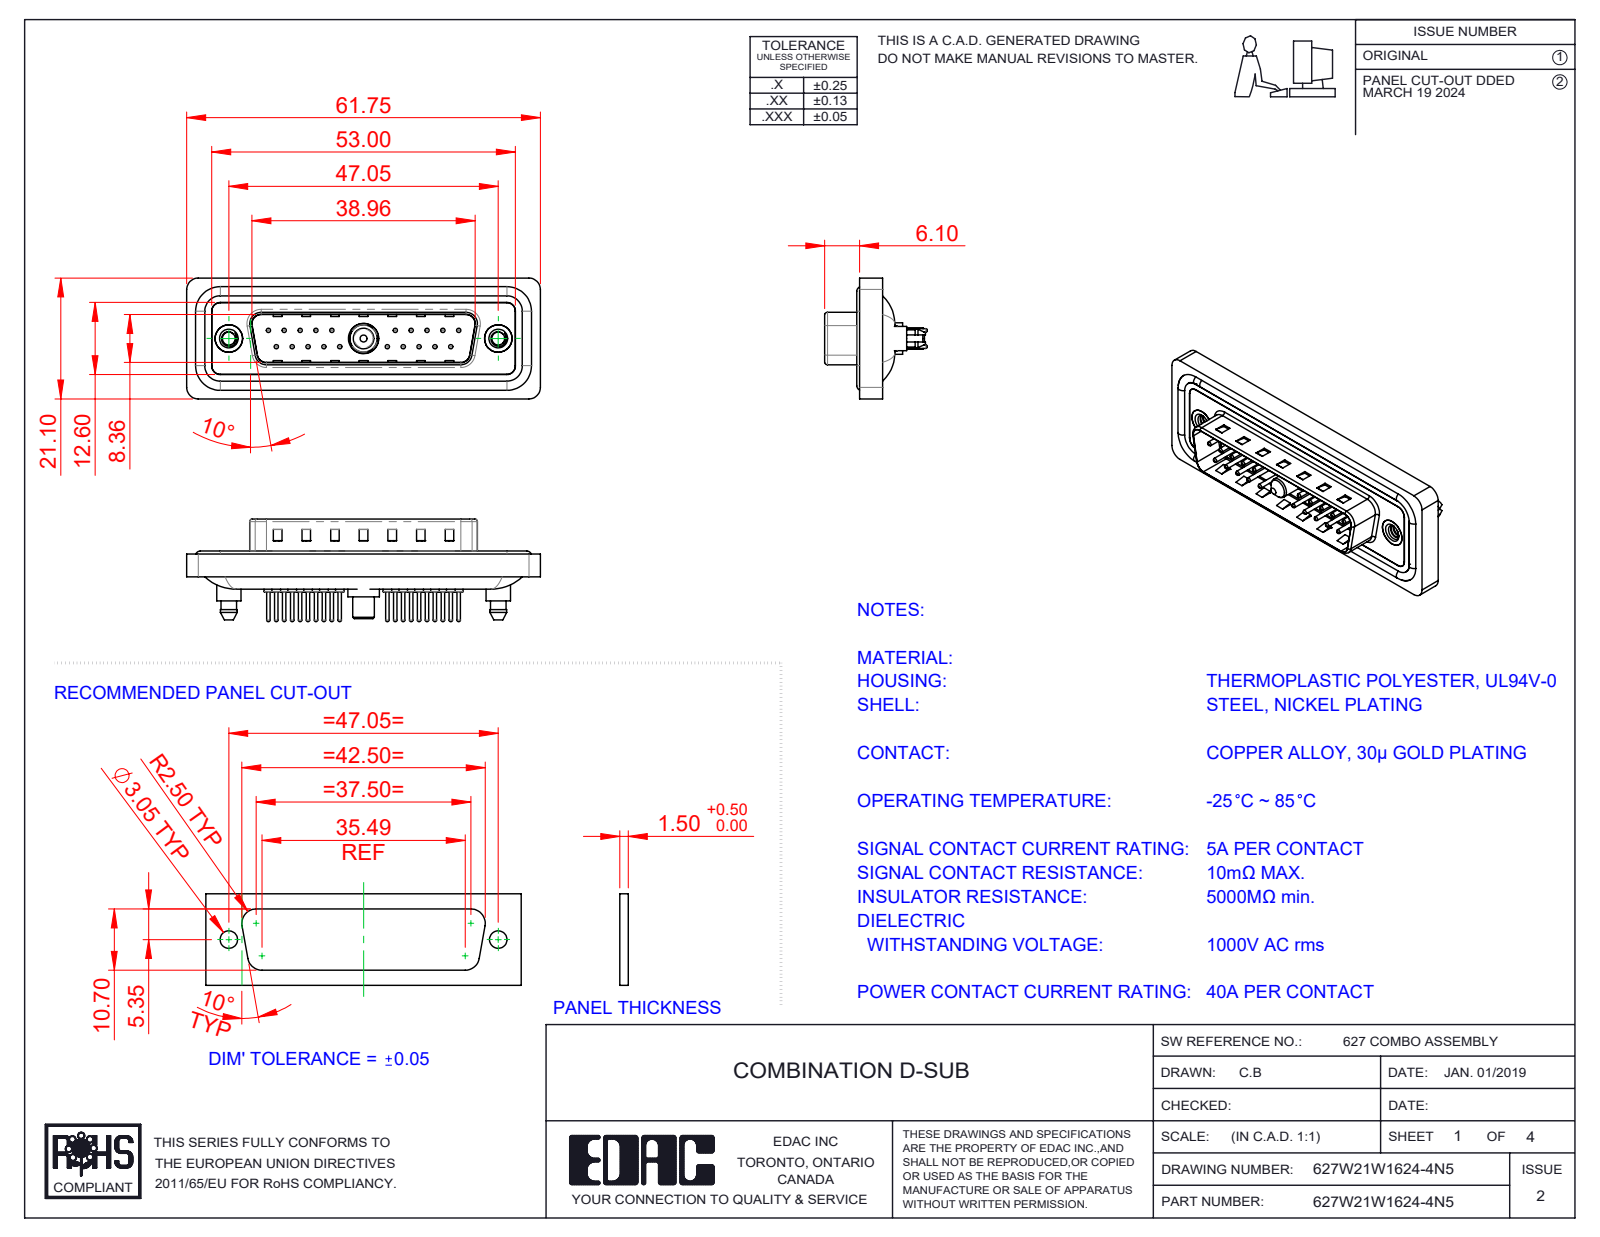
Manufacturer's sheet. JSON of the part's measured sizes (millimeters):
{"part_name": "627Combo Shell Rear_25 Contacts; 627Combo Contact Row 2_24; 627Combo Waterproof Housing_25 Contacts; 627W21W1624-4N5 (+5 more)", "step_written_by": "SolidWorks 2023 (CONFIG_CONTROL_DESIGN)", "units": "millimeters", "bodies": {"solids": 29, "faces": 1312, "planar": 375, "cylindrical": 519, "other": 418}, "overall_size": [61.75, 21.1, 17.9], "volume_mm3": 7350, "surface_area_mm2": 12297, "round_holes": [[0.75, 20], [1.6, 20], [2, 20], [2.26, 2], [4, 2], [4.8, 2], [5, 2], [4.85, 1], [5.3, 1]], "round_bosses_or_shafts": [[1.5, 20], [0.6, 20], [1.6, 4], [5.4, 2], [4.9, 2], [4.25, 2], [5.5, 1], [5.2, 1]], "partial_cylinders_radius": [[1.5, 24], [2, 18], [1.6, 10], [0.5, 8], [0.25, 4], [0.6, 4], [0.65, 4], [0.9, 4]], "face_to_face_distances": [0.4, 1.5, 1.1, 1.6, 3.1, 0.5, 2.9, 4.1, 0.82, 9.58], "hole_center_spacings": [3.16, 2.77, 5.54, 8.31, 5.04, 19.39, 20.97, 22.16]}
